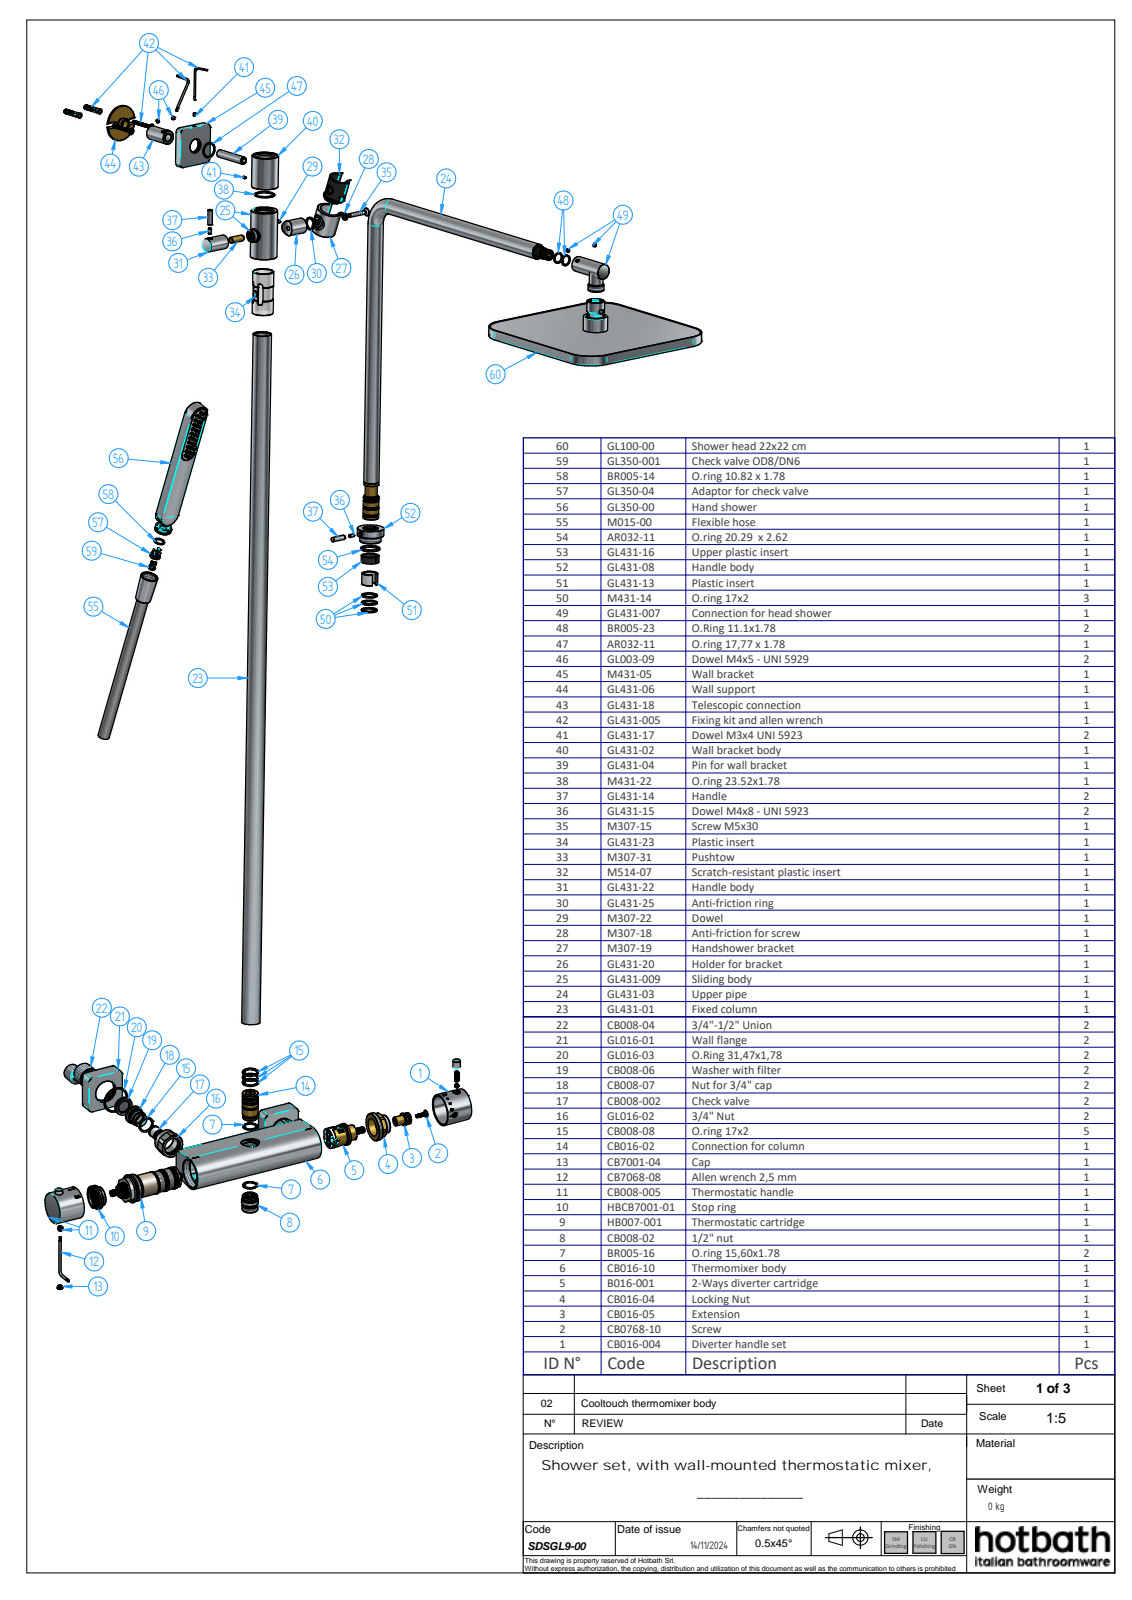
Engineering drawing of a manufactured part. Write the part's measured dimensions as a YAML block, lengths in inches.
part_name: "SDSGL9-00 NL Rel 2025; GL016-00 Rel1_oa_0; CB008-07; GL016-01 (+8 more)"
step_written_by: "Solid Edge (CONFIG_CONTROL_DESIGN)"
units: inches
bodies: {solids: 45, faces: 5892, planar: 2211, cylindrical: 1707, other: 1974}
overall_size: [57.618, 21.854, 10.211]
volume: 49.93
surface_area: 1215
round_holes:
  - {diameter: 0.128, count: 7}
  - {diameter: 0.126, count: 6}
  - {diameter: 0.728, count: 6}
  - {diameter: 0.276, count: 5}
  - {diameter: 0.354, count: 4}
  - {diameter: 0.65, count: 4}
  - {diameter: 0.097, count: 3}
  - {diameter: 0.163, count: 3}
  - {diameter: 0.402, count: 3}
  - {diameter: 0.827, count: 3}
  - {diameter: 0.059, count: 2}
  - {diameter: 0.079, count: 2}
round_bosses_or_shafts:
  - {diameter: 0.157, count: 5}
  - {diameter: 0.787, count: 4}
  - {diameter: 0.276, count: 4}
  - {diameter: 0.709, count: 3}
  - {diameter: 0.394, count: 3}
  - {diameter: 0.236, count: 3}
  - {diameter: 1.476, count: 2}
  - {diameter: 1.177, count: 2}
partial_cylinders:
  - {radius: 0.031, count: 400}
  - {radius: 0.008, count: 150}
  - {radius: 0.079, count: 113}
  - {radius: 0.02, count: 87}
  - {radius: 0.051, count: 40}
  - {radius: 0.012, count: 18}
  - {radius: 0.083, count: 14}
  - {radius: 0.197, count: 12}
face_to_face_distances: [0.039, 0.472, 0.512, 0.433, 0.295, 0.374, 0.217, 0.138, 0.177, 0.256]
hole_center_spacings: [1.893, 2.643, 2.677, 4.513, 4.685, 5.094, 6.397, 0.236]
